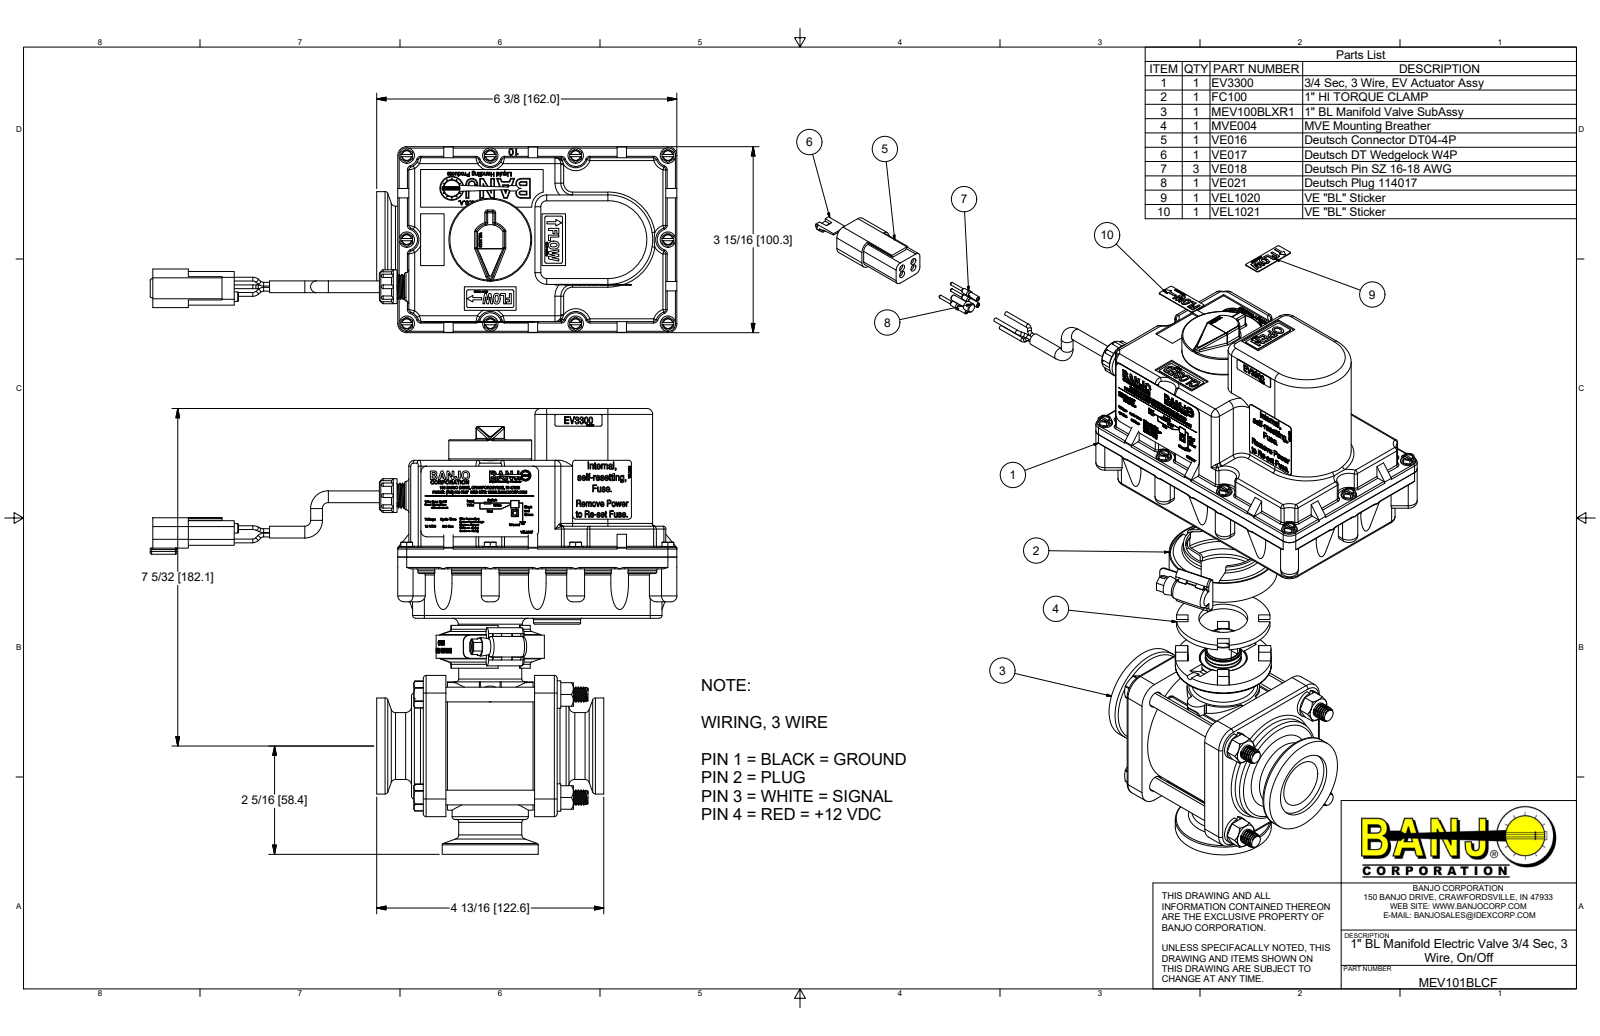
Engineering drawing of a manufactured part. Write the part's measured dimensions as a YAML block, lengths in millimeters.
part_name: "MEV101BLCF; MEV100BLXR1; MEV10354AB; MEV10354ABX (+8 more)"
step_written_by: "Autodesk Inventor 2017 (AUTOMOTIVE_DESIGN)"
units: millimeters
bodies: {solids: 80, faces: 13028, planar: 6404, cylindrical: 1818, other: 4806}
overall_size: [284.26, 240.47, 100.33]
volume: 946316
surface_area: 407331
round_holes:
  - {diameter: 2.79, count: 10}
  - {diameter: 3.81, count: 10}
  - {diameter: 4.06, count: 10}
  - {diameter: 5.08, count: 10}
  - {diameter: 1.32, count: 8}
  - {diameter: 2.01, count: 8}
  - {diameter: 1.19, count: 6}
  - {diameter: 3.05, count: 6}
  - {diameter: 4.47, count: 6}
  - {diameter: 0.38, count: 4}
  - {diameter: 0.76, count: 4}
  - {diameter: 6.41, count: 4}
round_bosses_or_shafts:
  - {diameter: 6.82, count: 60}
  - {diameter: 8.33, count: 10}
  - {diameter: 3.51, count: 10}
  - {diameter: 2.03, count: 9}
  - {diameter: 2.62, count: 8}
  - {diameter: 6.35, count: 7}
  - {diameter: 1.9, count: 5}
  - {diameter: 14.81, count: 4}
partial_cylinders:
  - {radius: 0.76, count: 151}
  - {radius: 1.52, count: 65}
  - {radius: 0.51, count: 62}
  - {radius: 0.89, count: 43}
  - {radius: 3.17, count: 40}
  - {radius: 8, count: 24}
  - {radius: 12.7, count: 24}
  - {radius: 1.59, count: 21}
face_to_face_distances: [3.17, 3.18, 82.04, 27.94, 5.08, 85.22, 19.81, 33.02, 20.07, 76.96]
hole_center_spacings: [42.68, 52.27, 42.78, 45.34, 60.36, 2.77, 12.5, 30.18]
